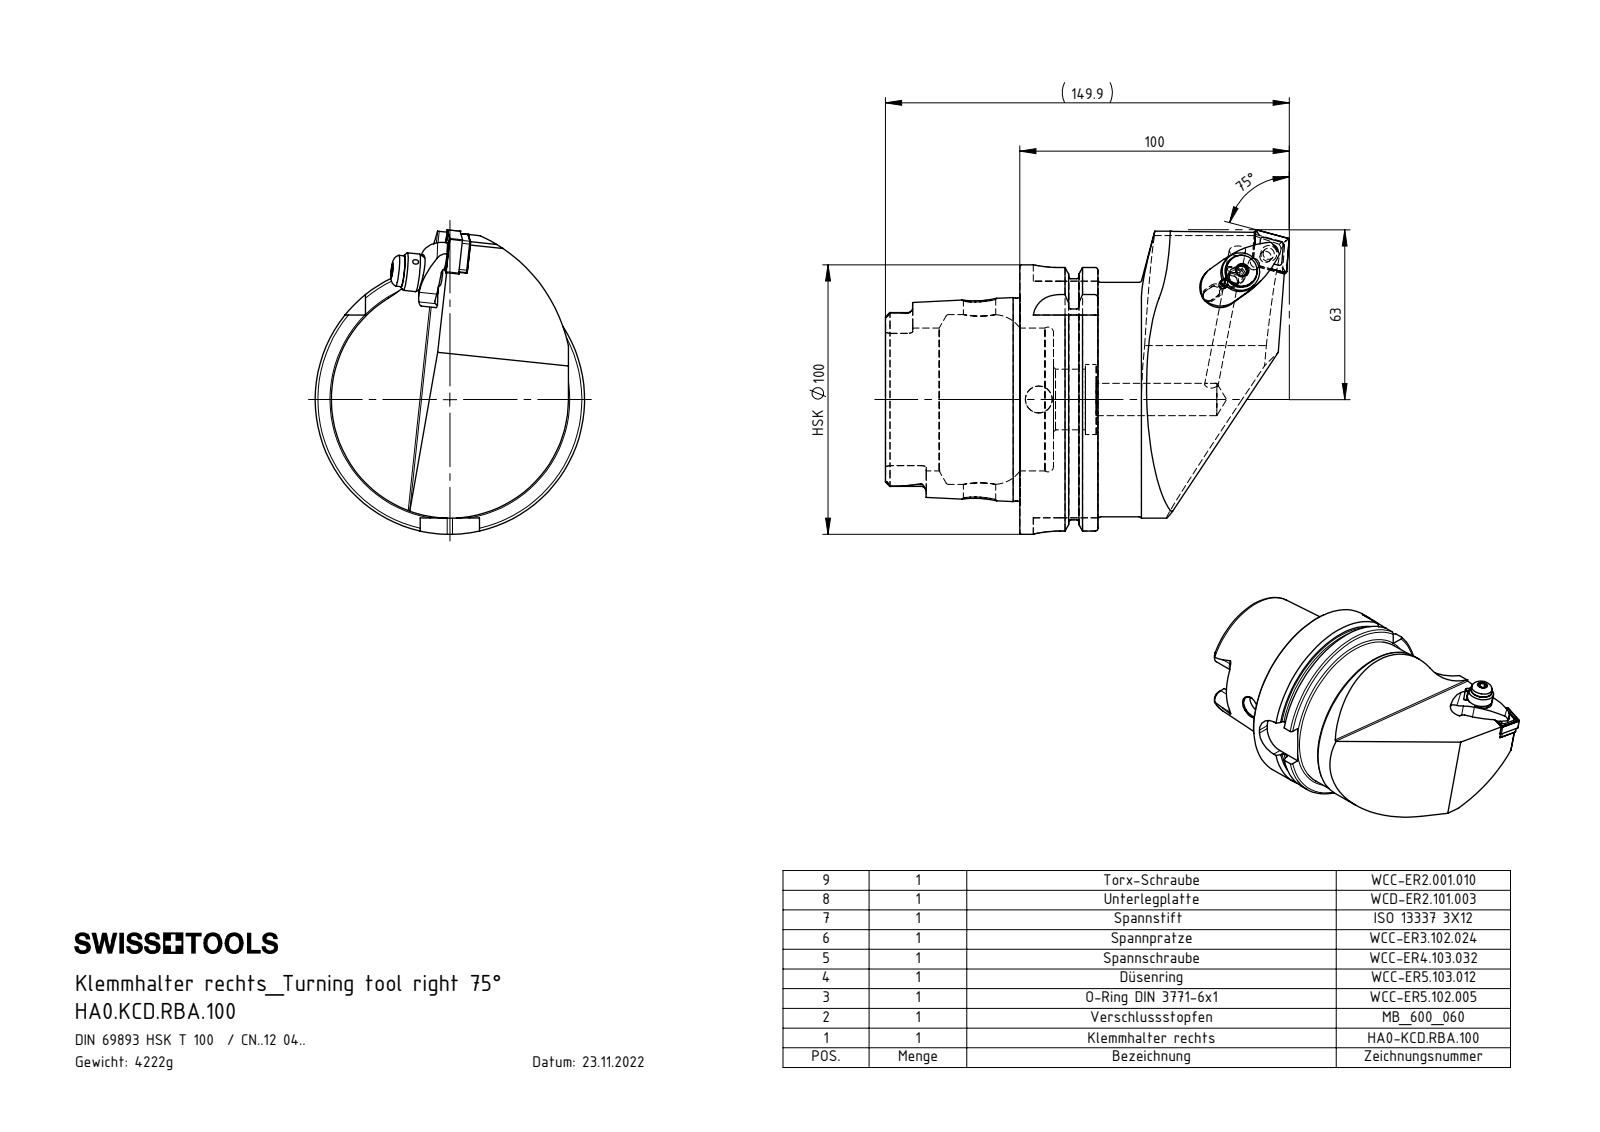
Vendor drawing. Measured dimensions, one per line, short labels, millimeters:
name: CNMG120404; WCC-ER5.103.012_A; WCC-ER5.102.005_A; ISO 13337 - 3 x 12_PreviewCfg (+7 more)
written by: SolidWorks 2017 (AUTOMOTIVE_DESIGN)
unit: mm
bodies: 11 solids, 474 faces (123 planar, 156 cylindrical, 195 other)
size: 149.86 × 112.96 × 100
volume: 537 079 mm³; area: 73 715 mm²
holes: 3× ⌀2, 3× ⌀5, 2× ⌀4.2, 2× ⌀7, 2× ⌀12, 1× ⌀2.4, 1× ⌀3, 1× ⌀4, 1× ⌀5.16, 1× ⌀6, 1× ⌀6.2, 1× ⌀6.4
bosses: 2× ⌀6, 1× ⌀100, 1× ⌀91.95, 1× ⌀87, 1× ⌀75.26, 1× ⌀14, 1× ⌀11.5, 1× ⌀7
rounds: 6× R0.39, 6× R1.9, 4× R0.4, 4× R0.69, 4× R1, 4× R10, 3× R40, 2× R0.69
face distances: 12.45, 28.95, 16.5, 49.9, 62.35, 78.85, 87.8, 78.2, 28.3, 15.85
hole spacings: 6.93, 6.98, 7.81, 8, 8.02, 8.2, 14.74, 14.8
